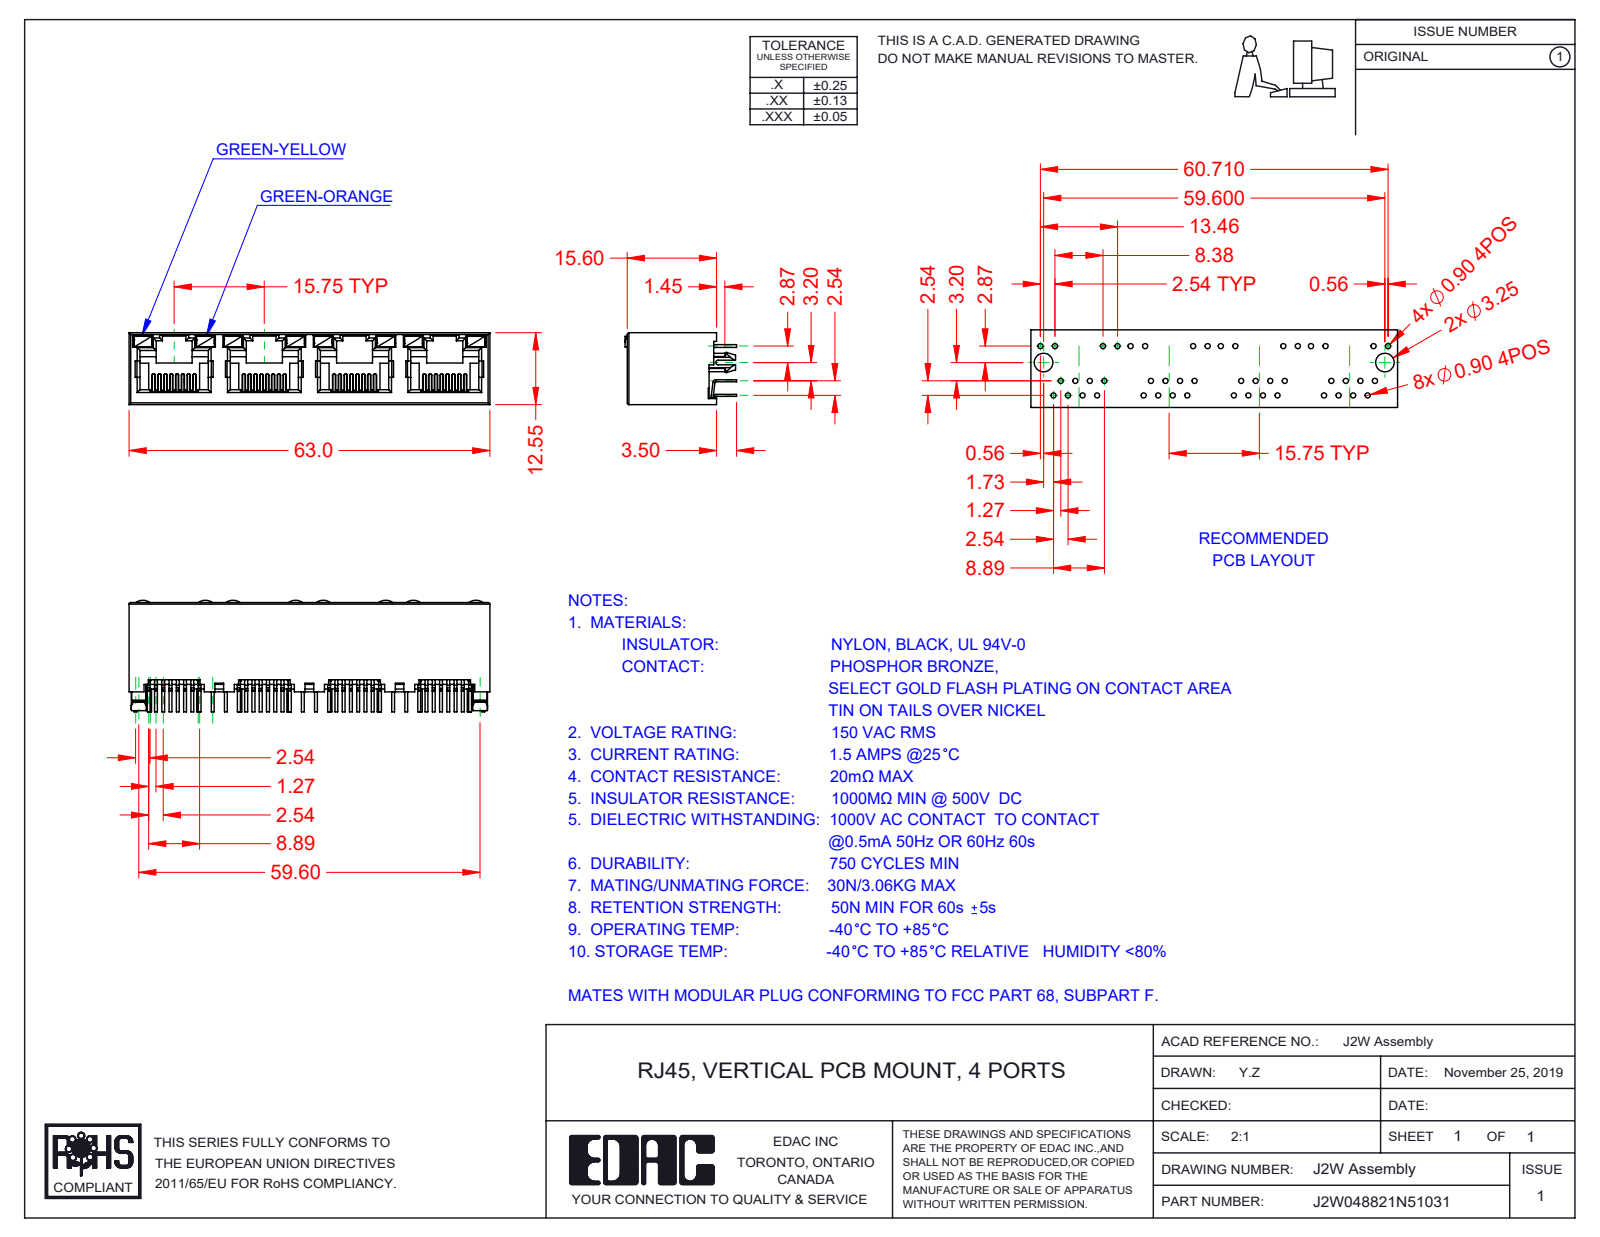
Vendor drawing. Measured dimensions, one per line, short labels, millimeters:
name: J2W048821N57131; 2W Insulator; 2W LED RH_7-Green-Orange; 2W Contact Lock (+2 more)
written by: SolidWorks 2016 (CONFIG_CONTROL_DESIGN)
unit: mm
bodies: 45 solids, 3143 faces (2600 planar, 485 cylindrical, 58 other)
size: 63 × 19.5 × 12.55
volume: 5 335 mm³; area: 13 144 mm²
rounds: 64× R0.15, 29× R0.2, 28× R0.5, 14× R0.3, 8× R0.45, 8× R2, 2× R0.25, 2× R1.5
face distances: 12.55, 11.9, 0.65, 15.75, 0.36, 1.5, 0.78, 0.6, 11.3, 31.5
